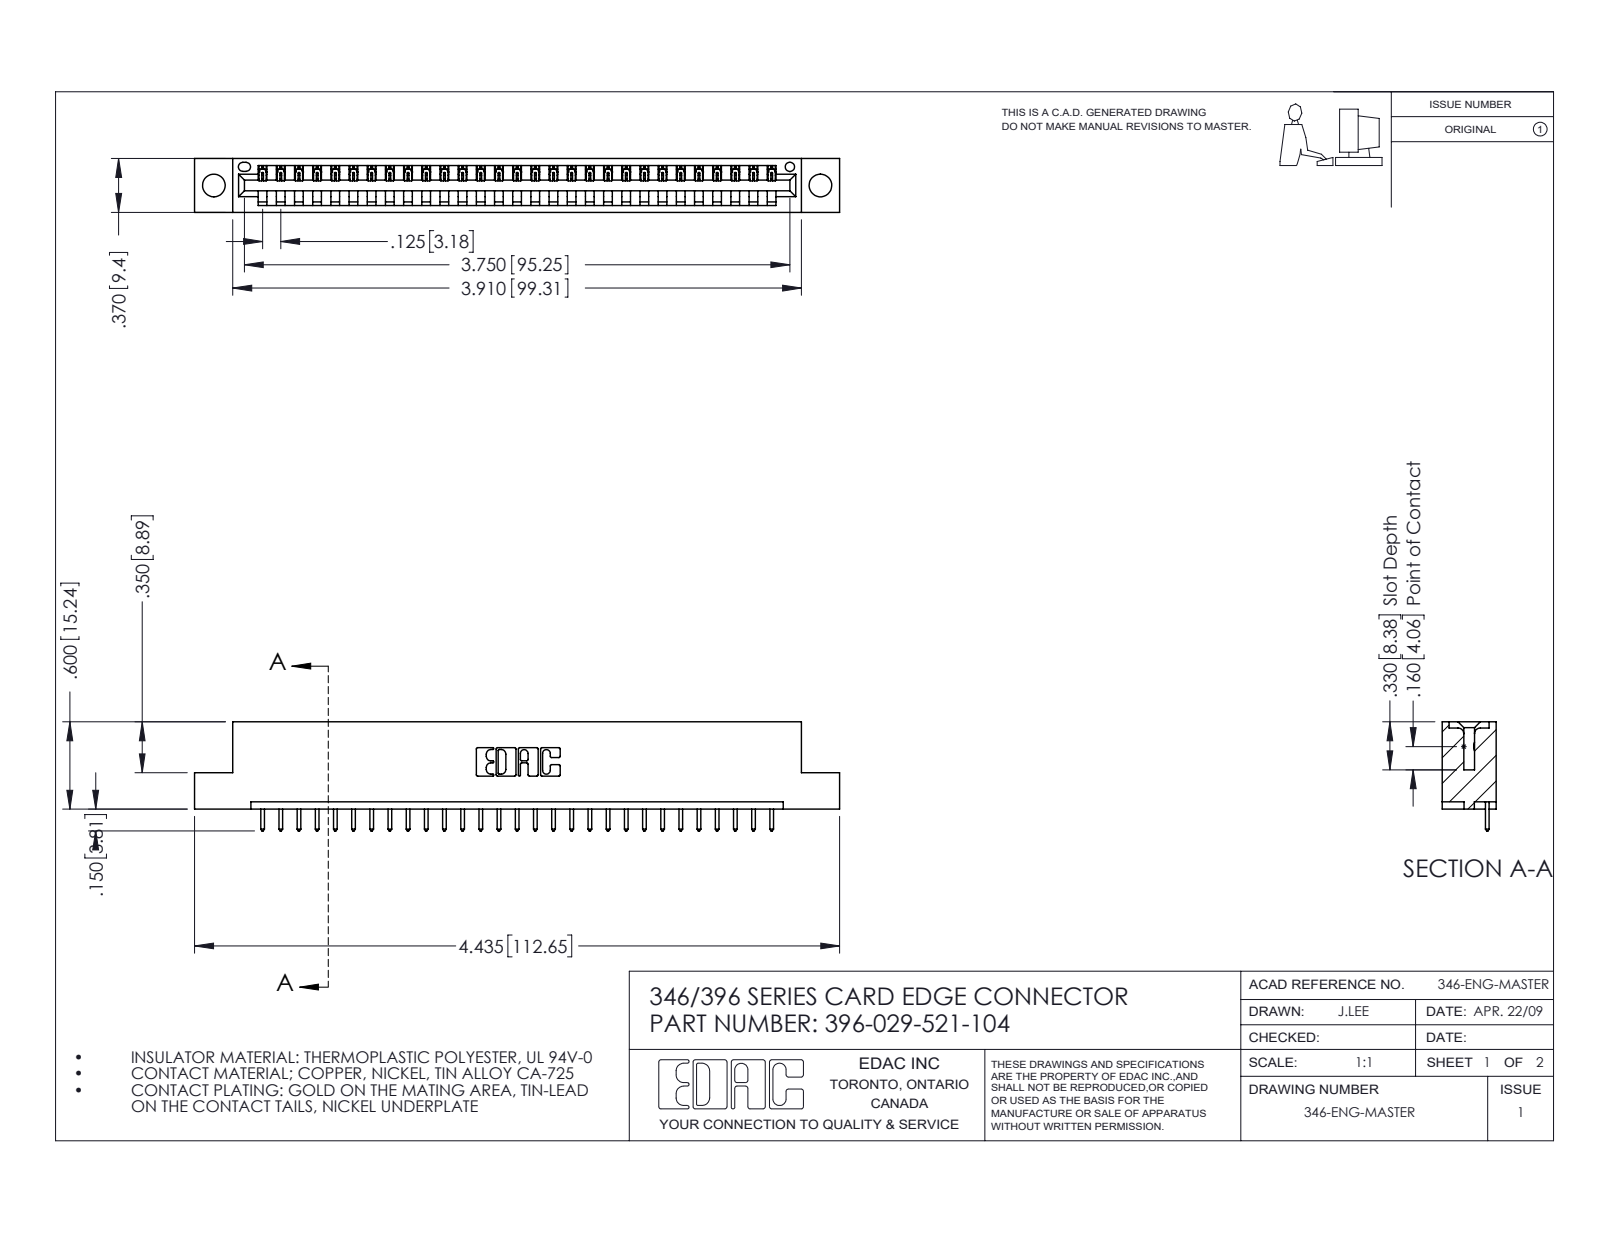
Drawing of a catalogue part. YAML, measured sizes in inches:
part_name: "346 Part_Flush Mounting Lugs - 0.156 Dia-TH; 345-292-001_345-293-121; 396-029-521-104"
step_written_by: "SolidWorks 2016 (CONFIG_CONTROL_DESIGN)"
units: inches
bodies: {solids: 30, faces: 1804, planar: 1236, cylindrical: 568, other: 0}
overall_size: [4.435, 0.75, 0.37]
volume: 0.642
surface_area: 19.36
round_holes:
  - {diameter: 0.156, count: 2}
  - {diameter: 0.064, count: 1}
partial_cylinders:
  - {radius: 0.006, count: 58}
  - {radius: 0.01, count: 58}
  - {radius: 0.01, count: 22}
  - {radius: 0.007, count: 6}
  - {radius: 0.031, count: 6}
  - {radius: 0.026, count: 3}
  - {radius: 0.031, count: 2}
  - {radius: 0.04, count: 2}
face_to_face_distances: [0.048, 0.322, 0.37, 0.25, 0.072, 0.298, 0.025, 0.148, 0.222, 0.1]
hole_center_spacings: [0.246, 3.962, 4.17]
